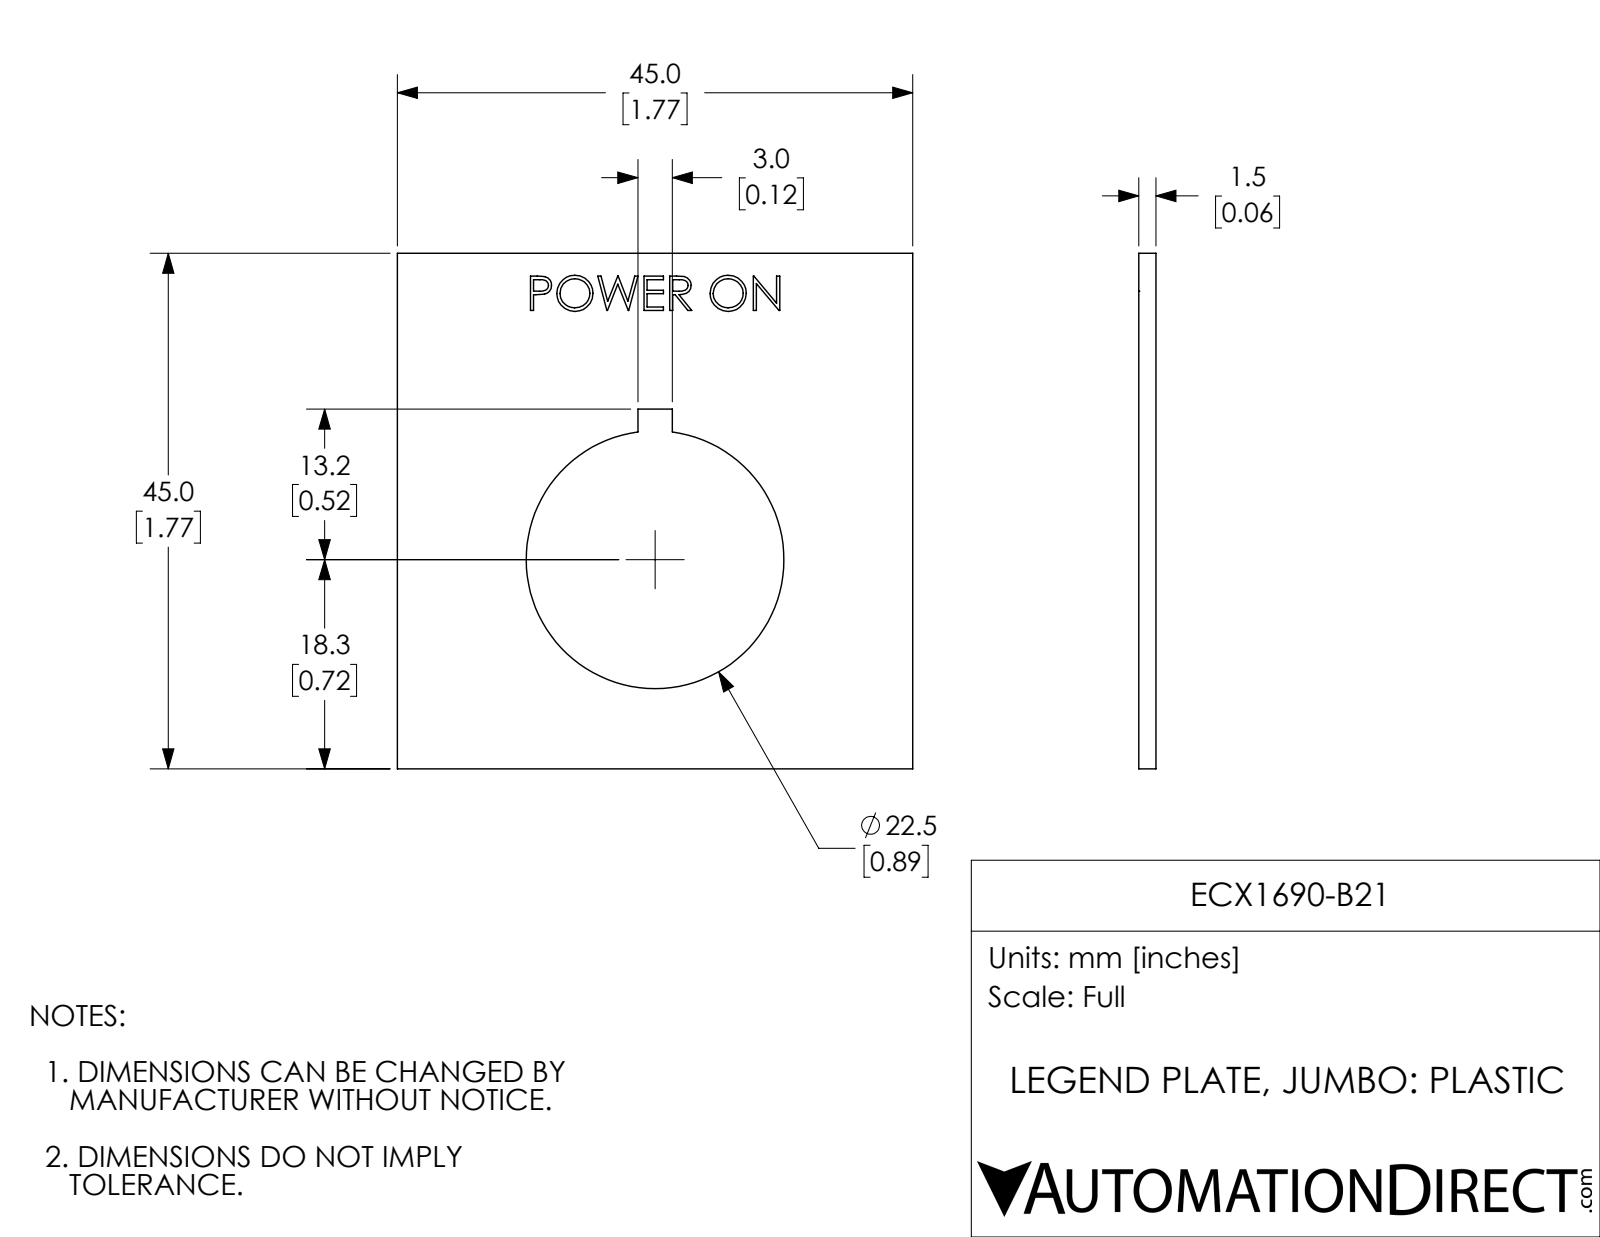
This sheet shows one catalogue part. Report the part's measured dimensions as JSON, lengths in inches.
{"part_name": "ECX1690-B21", "step_written_by": "SolidWorks 2018 (AUTOMOTIVE_DESIGN)", "units": "inches", "bodies": {"solids": 1, "faces": 104, "planar": 74, "cylindrical": 3, "other": 27}, "overall_size": [1.772, 1.772, 0.059], "volume_in3": 0.148, "surface_area_in2": 5.624, "round_holes": [[0.886, 1]], "face_to_face_distances": [0.059, 1.772, 0.058, 0.827, 0.945, 1.236, 0.535, 0.118, 0.457, 1.314]}
